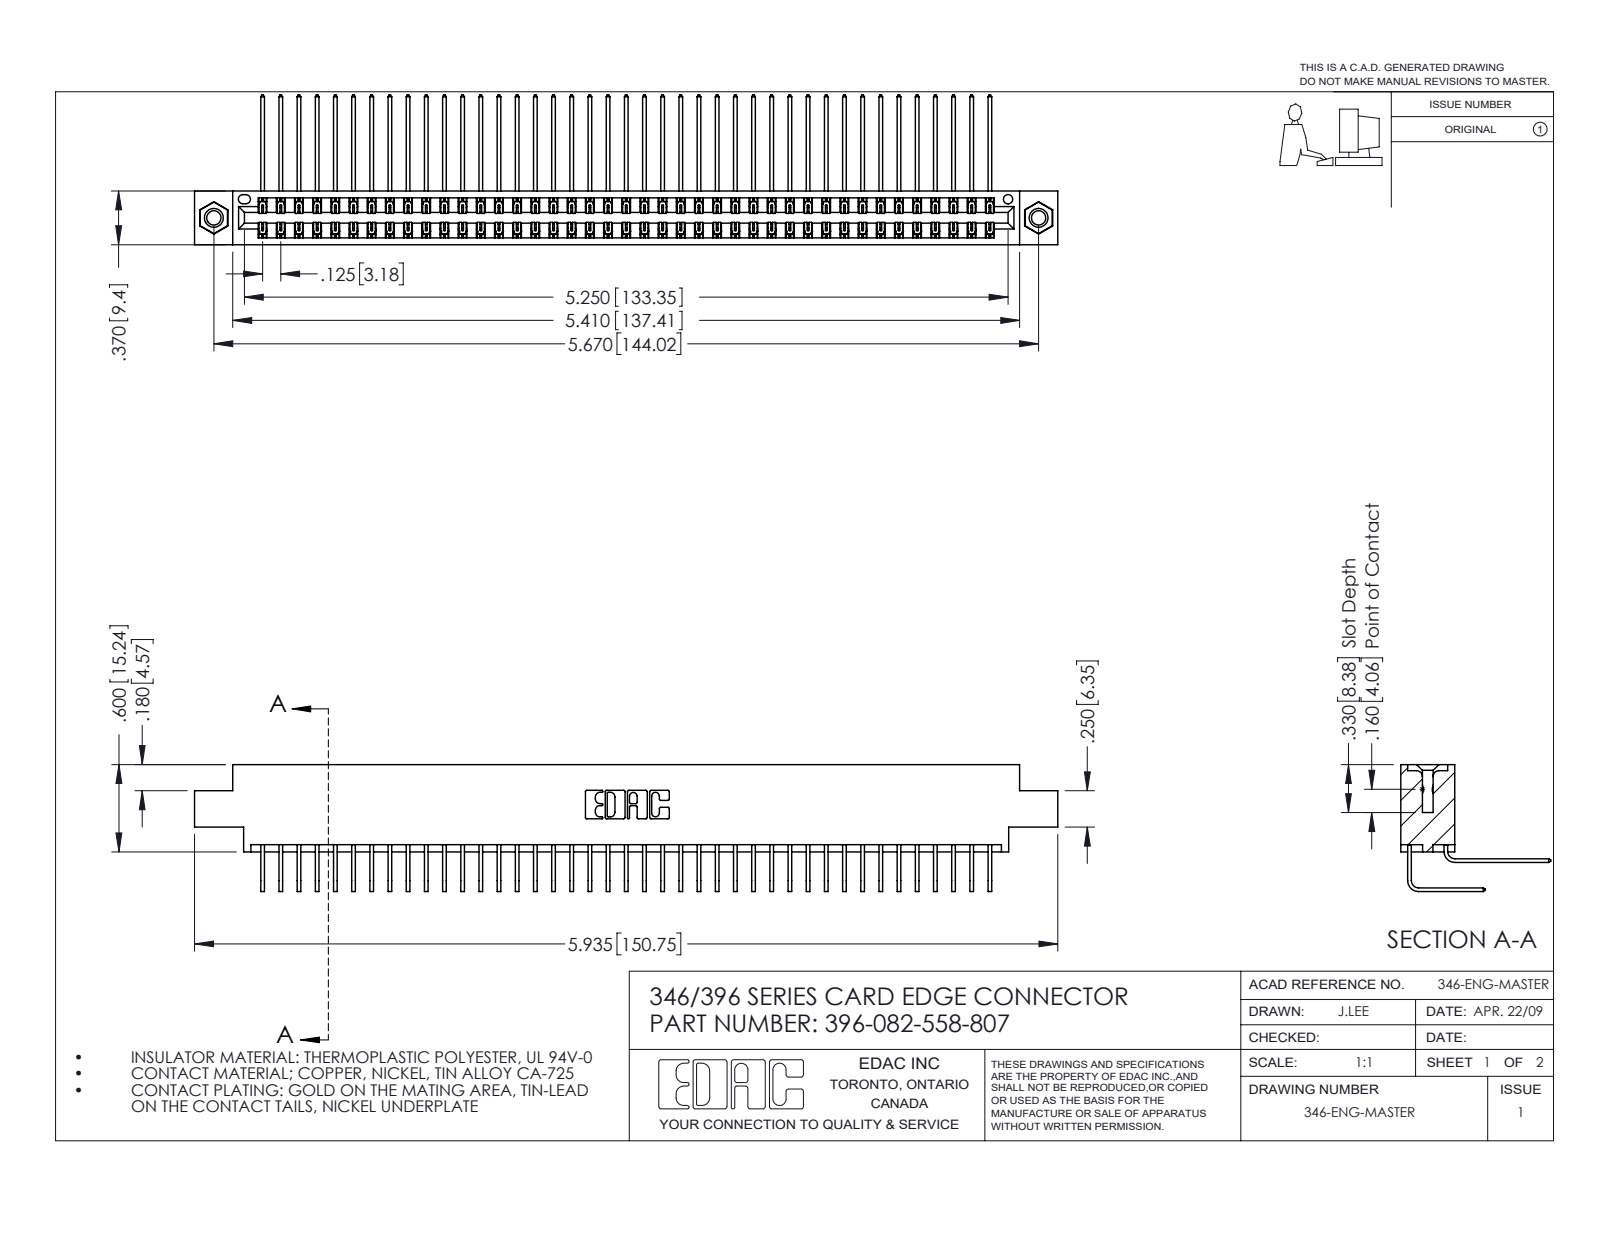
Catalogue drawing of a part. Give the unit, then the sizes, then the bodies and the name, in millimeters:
Units: millimetres
Overall size (bounding box): 150.7 × 26.2 × 22.2
Round holes (diameter × count): ⌀2.5 ×2, ⌀3.2 ×2, ⌀4 ×2, ⌀1.6 ×1
Round bosses / shafts (diameter × count): ⌀3.9 ×2
Partial cylindrical surfaces — rounded edges, fillets, slot ends (radius × count): R0.2 ×123, R0.3 ×22, R0.2 ×6, R0.8 ×6, R0.7 ×3, R0.4 ×2, R0.6 ×2, R0.6 ×2
Main face-to-face distances: 8.2, 1.2, 0.6, 9.4, 6.4, 7.6, 1.8, 7, 5.6, 3.8
Hole centre spacings: 6.2, 138.7, 144
Volume: 15 000 mm³ · Surface area: 23 080 mm²
Bodies: 85 solids, 4614 faces (3146 planar, 1452 cylindrical, 16 other)
Part name (STEP PRODUCT): 346 Part_0.170 Offset - 0.156 Dia-TI; 396-082-558-807; 345-292-001_558 559 Tail - 1; 345-250-001_345-250-005-103 (+1 more)
STEP written by: SolidWorks 2016 (CONFIG_CONTROL_DESIGN)
